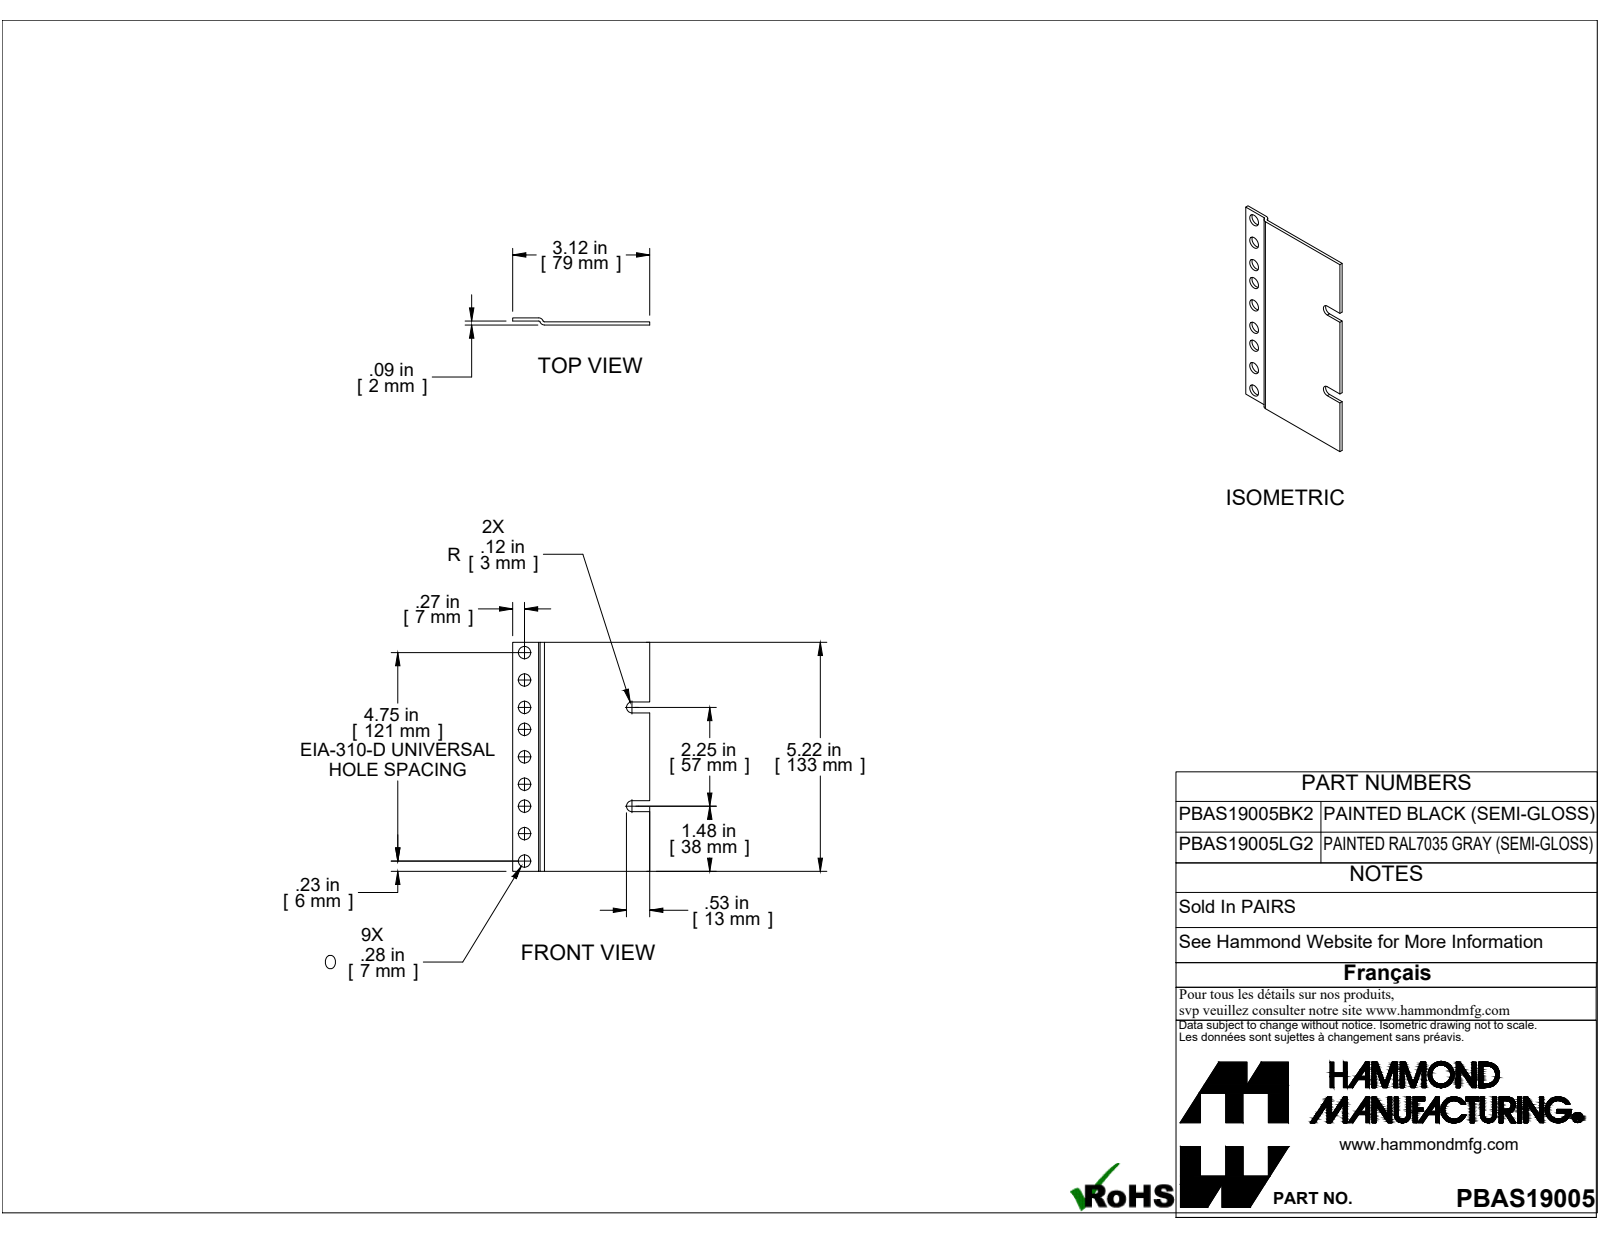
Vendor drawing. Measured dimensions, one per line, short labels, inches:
name: PBAS19005LG2
written by: SolidWorks 2019 (CONFIG_CONTROL_DESIGN)
unit: in
bodies: 1 solid, 29 faces (14 planar, 15 cylindrical, 0 other)
size: 5.218 × 3.125 × 0.162
volume: 1.13 in³; area: 33.3 in²
holes: 9× ⌀0.281
rounds: 2× R0.036, 2× R0.108, 2× R0.125
face distances: 0.072, 0.09, 0.162, 0.018, 0.09, 0.072, 3.125, 5.218, 1.359, 3.859
hole spacings: 0.625, 1.125, 1.75, 0.5, 0.625, 1.25, 1.75, 2.375
